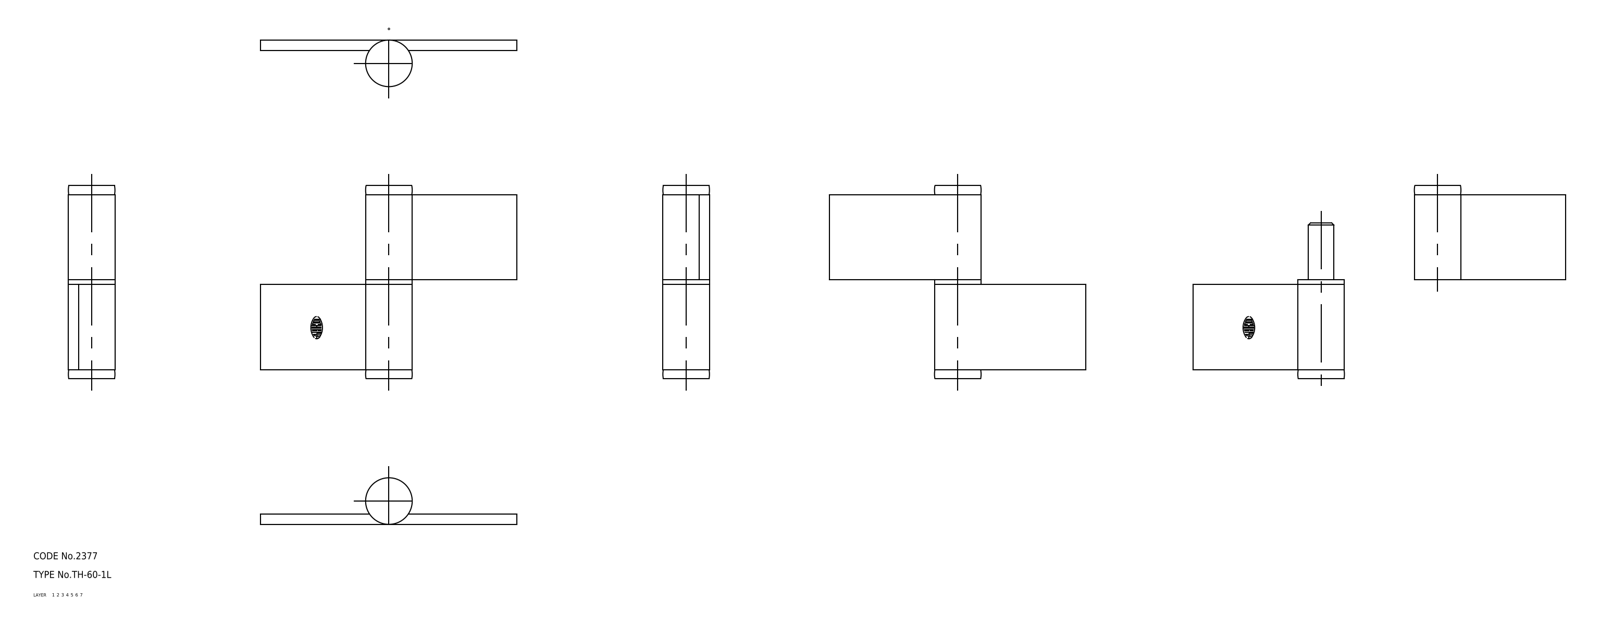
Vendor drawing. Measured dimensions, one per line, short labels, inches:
name: hinge piece; washer; shaft; rivet (+1 more)
written by: CADfix (AUTOMOTIVE_DESIGN)
unit: in
bodies: 5 solids, 34 faces (0 planar, 0 cylindrical, 34 other)
size: 4.331 × 3.268 × 0.787
volume: 2.526 in³; area: 32.95 in²
